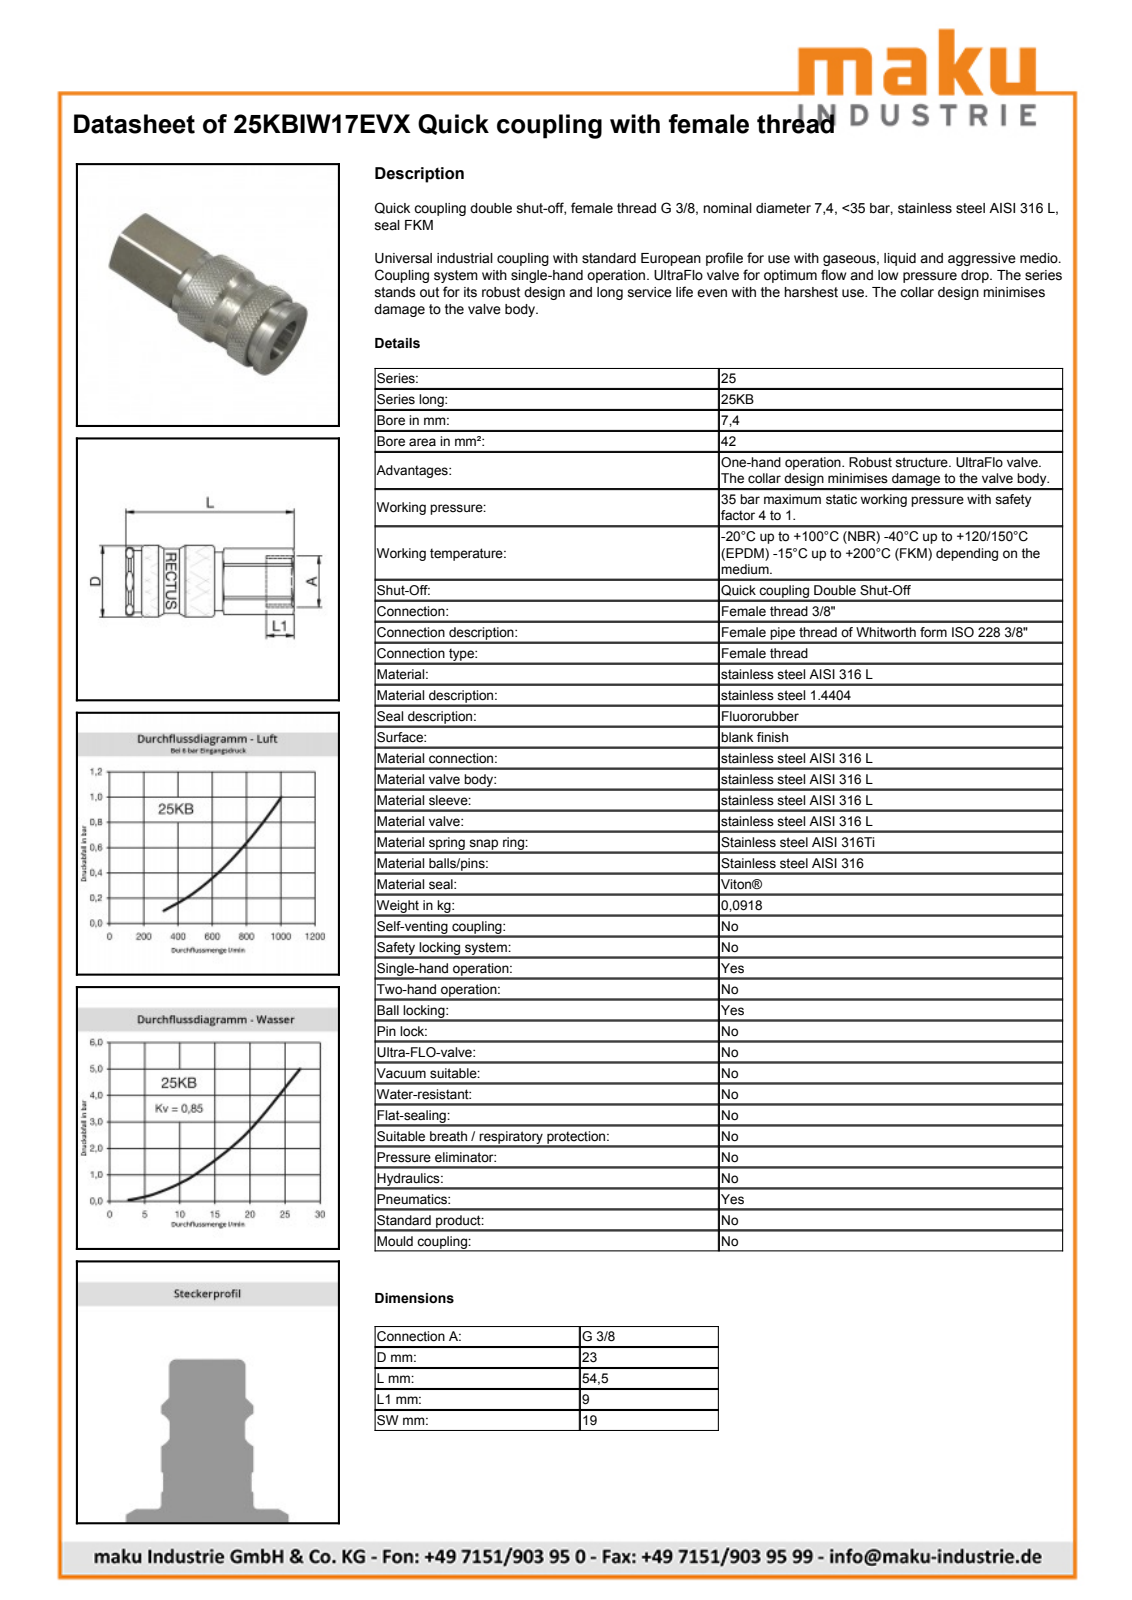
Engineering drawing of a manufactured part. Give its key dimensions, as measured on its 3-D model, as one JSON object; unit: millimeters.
{"part_name": "D111973", "step_written_by": "Autodesk Inventor 2013 (AUTOMOTIVE_DESIGN)", "units": "millimeters", "bodies": {"solids": 2, "faces": 608, "planar": 209, "cylindrical": 77, "other": 322}, "overall_size": [57.5, 23.15, 23.15], "volume_mm3": 18639, "surface_area_mm2": 7941, "round_holes": [[16, 1], [17.25, 1], [19.35, 1], [20.05, 1]], "round_bosses_or_shafts": [[23.15, 1], [21, 1], [20, 1], [18.95, 1], [15.3, 1]], "partial_cylinders_radius": [[10.4, 1], [10.7, 1], [11, 1]], "face_to_face_distances": [19, 57.5, 28.75, 1, 20, 24.5, 33, 5.25, 19.25, 4.25]}
